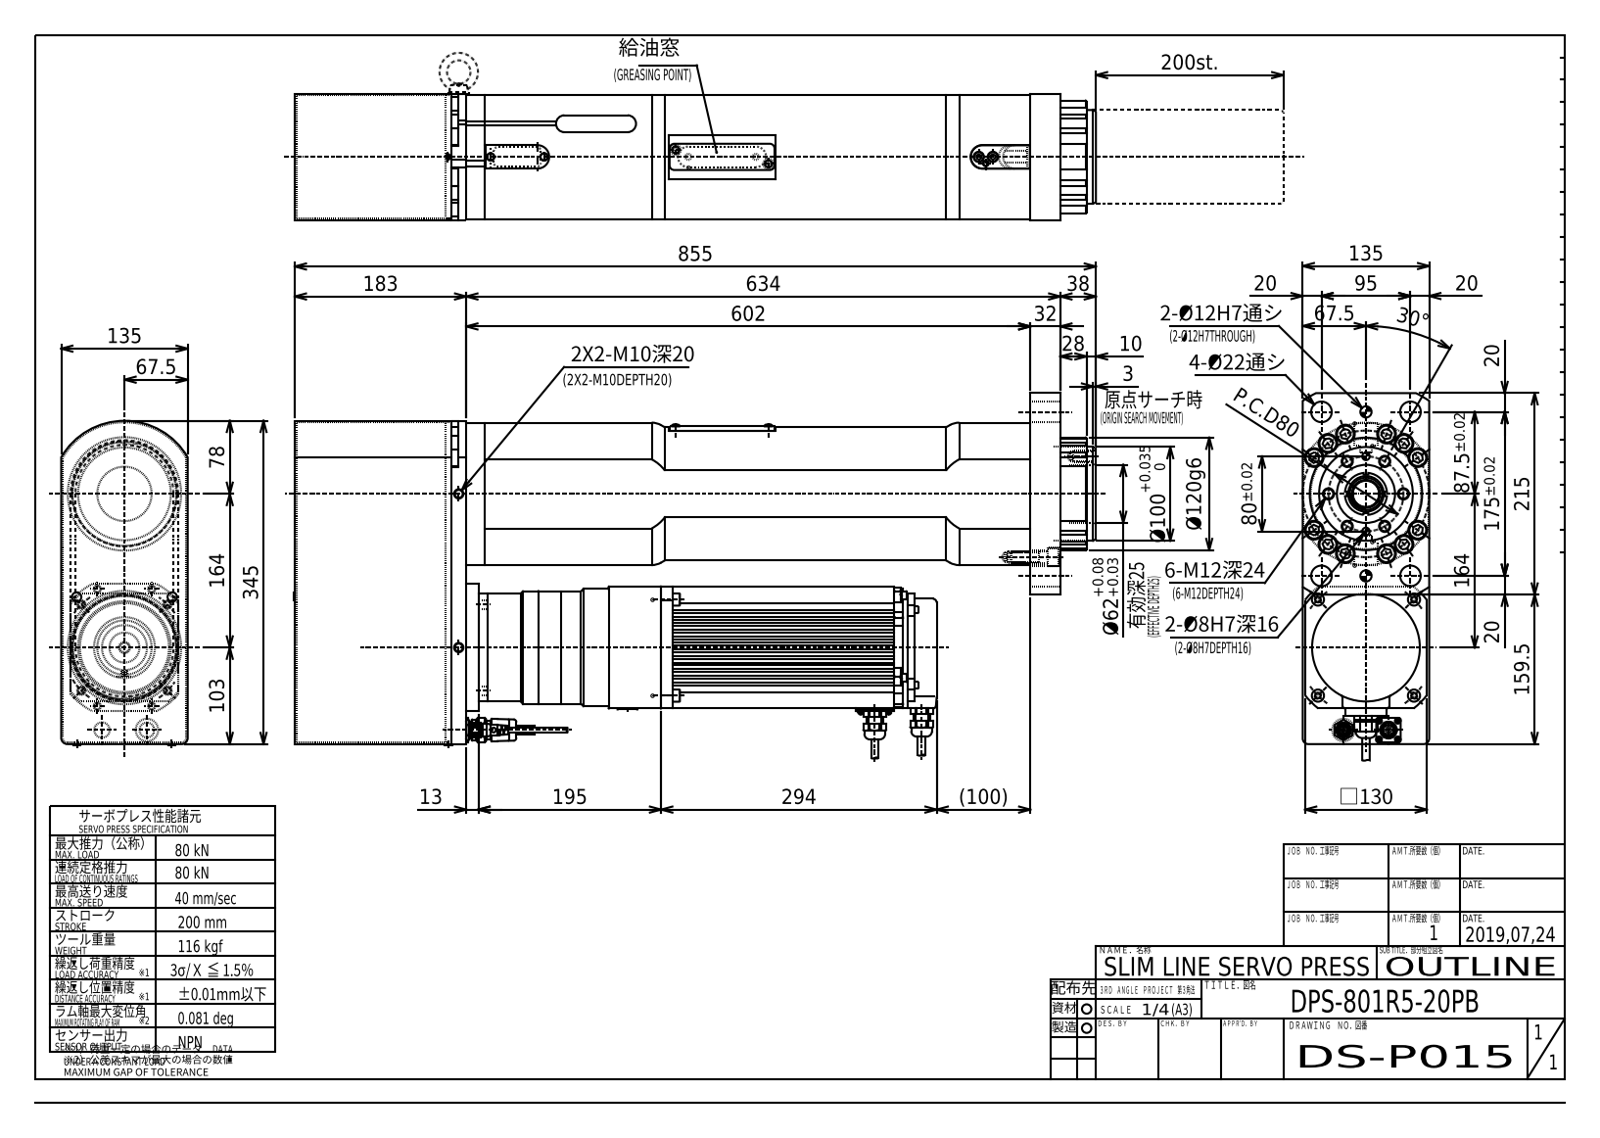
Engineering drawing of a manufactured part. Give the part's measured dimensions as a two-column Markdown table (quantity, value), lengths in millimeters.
| quantity | value |
| --- | --- |
| part name | DPS-801R5-20PB(DS-P015)_OUTLINE; DS-P001-02+A_U |
| STEP written by | Autodesk Inventor 2015 (AUTOMOTIVE_DESIGN) |
| units | millimeters |
| bodies | 3 solids, 1199 faces (676 planar, 385 cylindrical, 138 other) |
| overall size | 855 × 388.51 × 135 |
| volume | 25 740 000 mm³ |
| surface area | 1 374 000 mm² |
| round holes (diameter × count) | 6.65 × 12, 3.24 × 7, 10.11 × 6, 12 × 6, 3 × 4, 4.5 × 4, 4.92 × 4, 8 × 4, 9 × 4, 9.1 × 4, 22 × 4, 11 × 3 |
| round bosses / shafts (diameter × count) | 18 × 9, 6 × 5, 8.5 × 4, 4 × 4, 120 × 2, 10 × 2, 142 × 1, 125 × 1 |
| partial cylindrical surfaces (radius × count) | 5 × 49, 2 × 26, 0.5 × 8, 1 × 8, 10 × 7, 2.5 × 6, 3 × 5, 4 × 5 |
| main face-to-face distances | 135, 3, 6, 71, 68, 9, 65, 25, 28, 74 |
| hole center spacings | 40, 97.37, 102.54, 69.28, 125.2, 47.5, 7.51, 10.26 |
